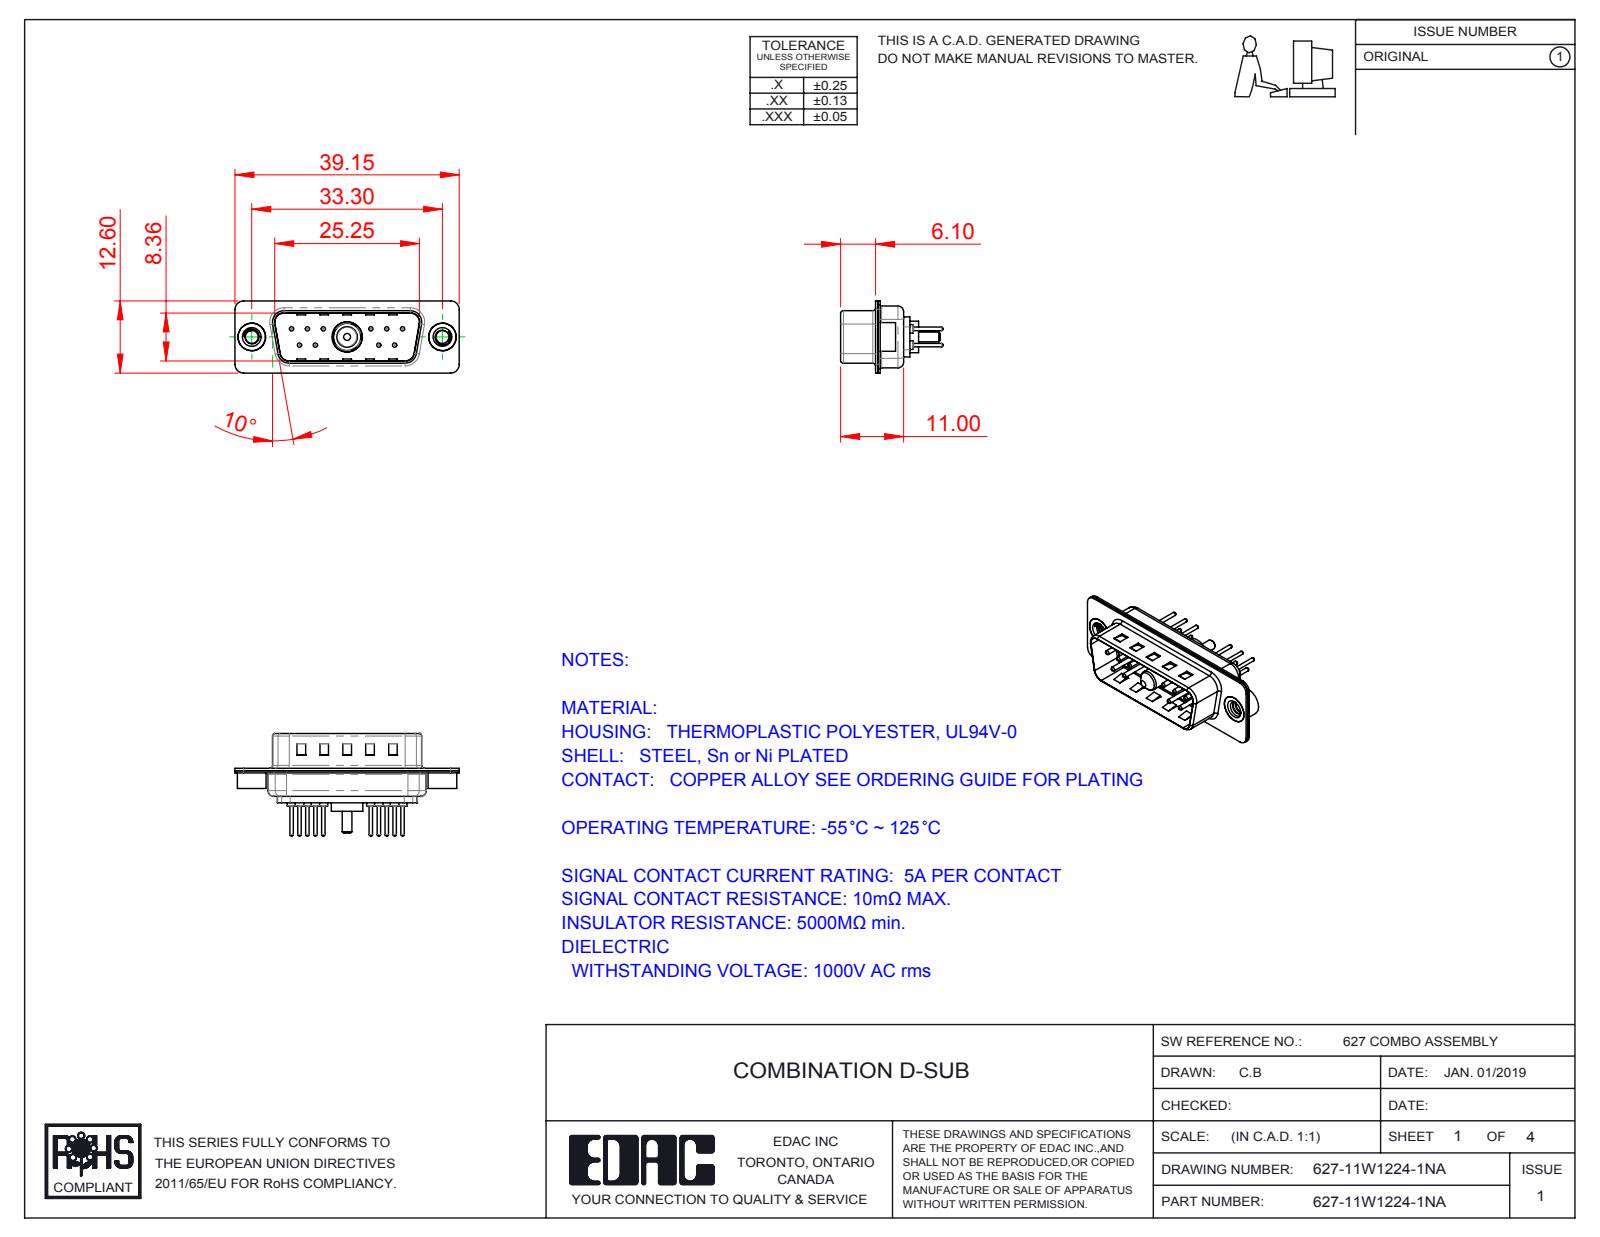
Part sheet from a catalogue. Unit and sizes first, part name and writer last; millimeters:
Units: millimetres
Overall size (bounding box): 39.15 × 17.9 × 12.6
Round holes (diameter × count): ⌀0.75 ×10, ⌀1.6 ×10, ⌀2 ×10, ⌀2.26 ×2, ⌀4 ×2, ⌀4.8 ×2, ⌀4.85 ×1, ⌀5.3 ×1
Round bosses / shafts (diameter × count): ⌀1.5 ×10, ⌀0.6 ×10, ⌀5 ×2, ⌀4.9 ×2, ⌀5.5 ×1, ⌀5.2 ×1, ⌀4.75 ×1, ⌀3.75 ×1
Partial cylindrical surfaces — rounded edges, fillets, slot ends (radius × count): R1.5 ×20, R2 ×12, R0.5 ×8, R1.6 ×8, R1 ×7, R0.25 ×4, R0.6 ×4, R0.65 ×4
Main face-to-face distances: 0.4, 0.82, 9.58, 8.76, 0.8, 1.5, 5.6, 1.4, 5.2, 6
Hole centre spacings: 3.16, 2.77, 13.85, 11.08, 16.62, 5.03, 5.04, 5.54
Volume: 1 898 mm³ · Surface area: 4 776 mm²
Bodies: 17 solids, 762 faces (228 planar, 297 cylindrical, 237 other)
Part name (STEP PRODUCT): 627Combo Housing_11W1; Power Pin_10A S; 627Combo Threaded Rivet_A; 627Combo Contact Row 2_24 (+5 more)
STEP written by: SolidWorks 2016 (CONFIG_CONTROL_DESIGN)
